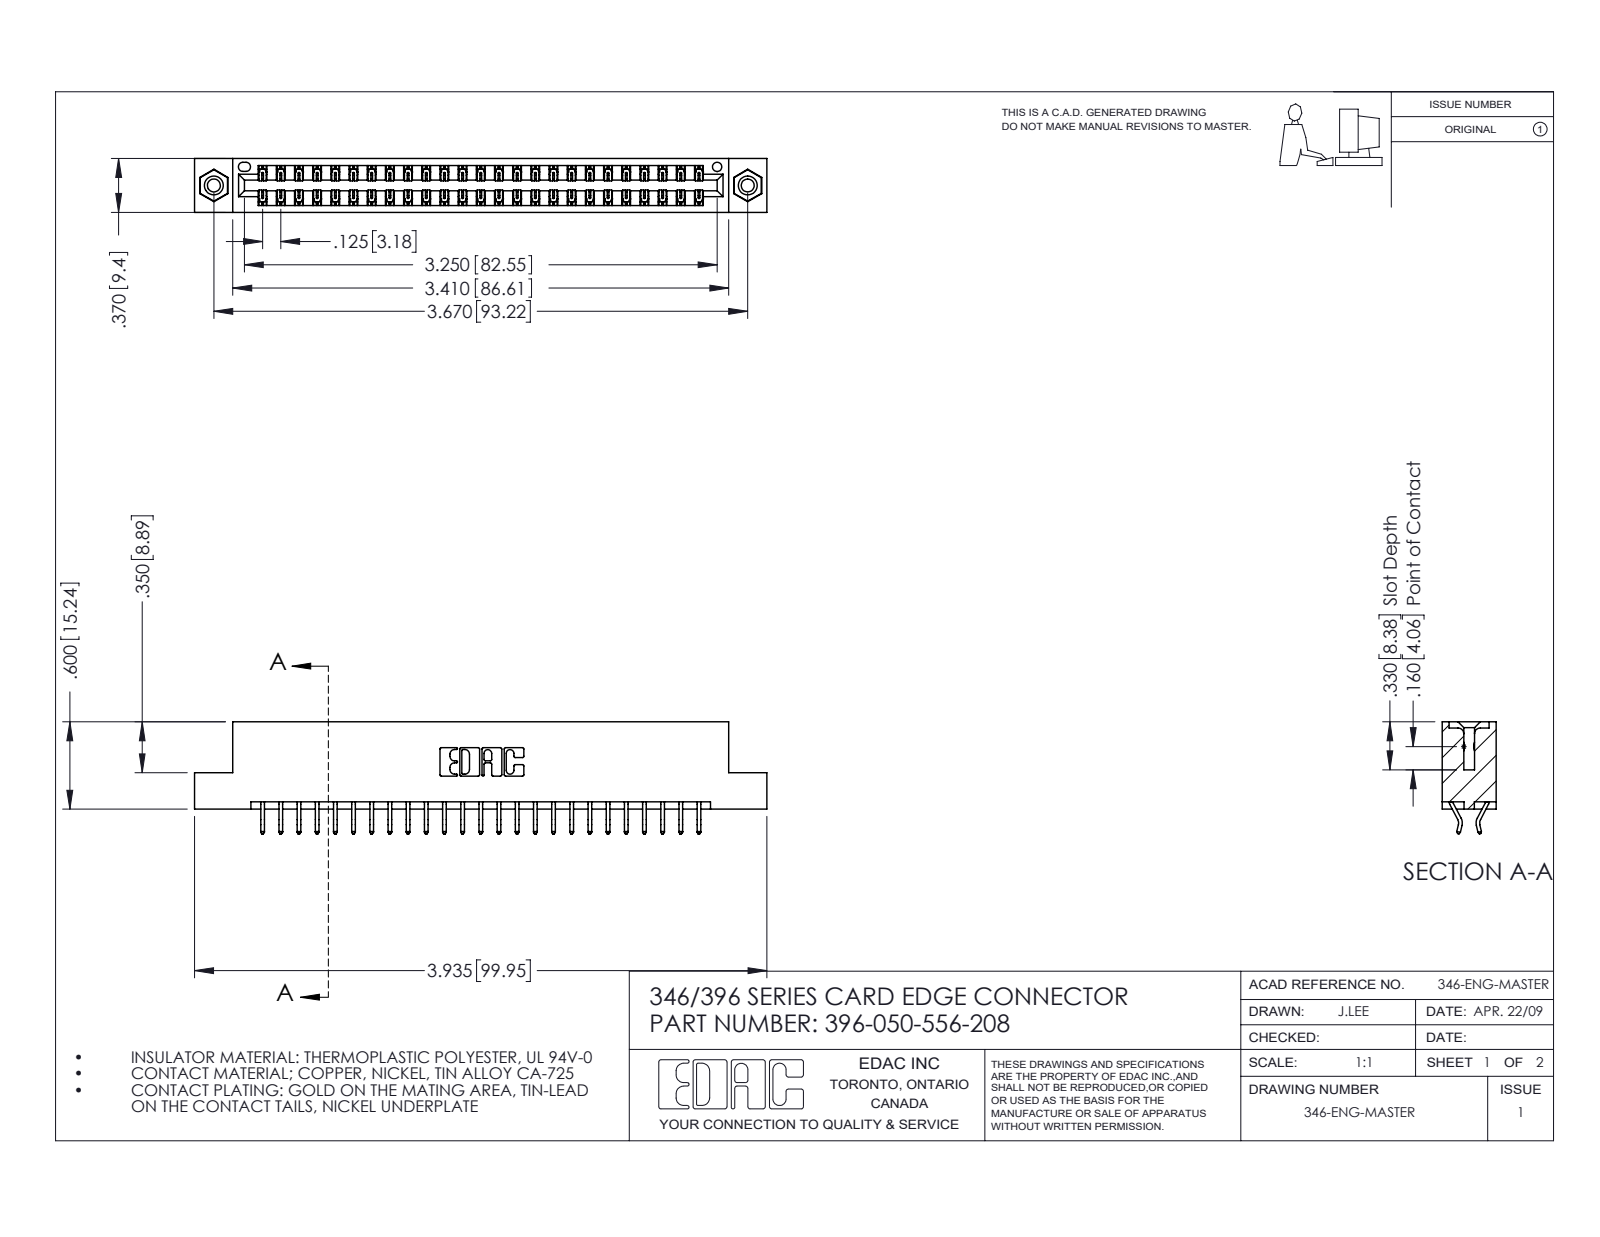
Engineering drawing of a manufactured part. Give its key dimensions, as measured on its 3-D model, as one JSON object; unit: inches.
{"part_name": "345-250-001_345-250-003-102; 345-292-001_556 Tail; 396-050-556-208; 346 Part_Flush Mounting Lugs - 0.156 Dia-TI", "step_written_by": "SolidWorks 2016 (CONFIG_CONTROL_DESIGN)", "units": "inches", "bodies": {"solids": 53, "faces": 3082, "planar": 2058, "cylindrical": 1008, "other": 16}, "overall_size": [3.935, 0.77, 0.37], "volume_in3": 0.586, "surface_area_in2": 20.01, "round_holes": [[0.089, 2], [0.125, 2], [0.156, 2], [0.064, 1]], "round_bosses_or_shafts": [[0.155, 2]], "partial_cylinders_radius": [[0.006, 75], [0.01, 22], [0.007, 6], [0.031, 6], [0.026, 3], [0.01, 2], [0.014, 2], [0.022, 2]], "face_to_face_distances": [0.048, 0.322, 0.37, 0.25, 0.025, 0.072, 0.298, 0.275, 0.148, 0.222], "hole_center_spacings": [0.246, 3.462, 3.67]}
